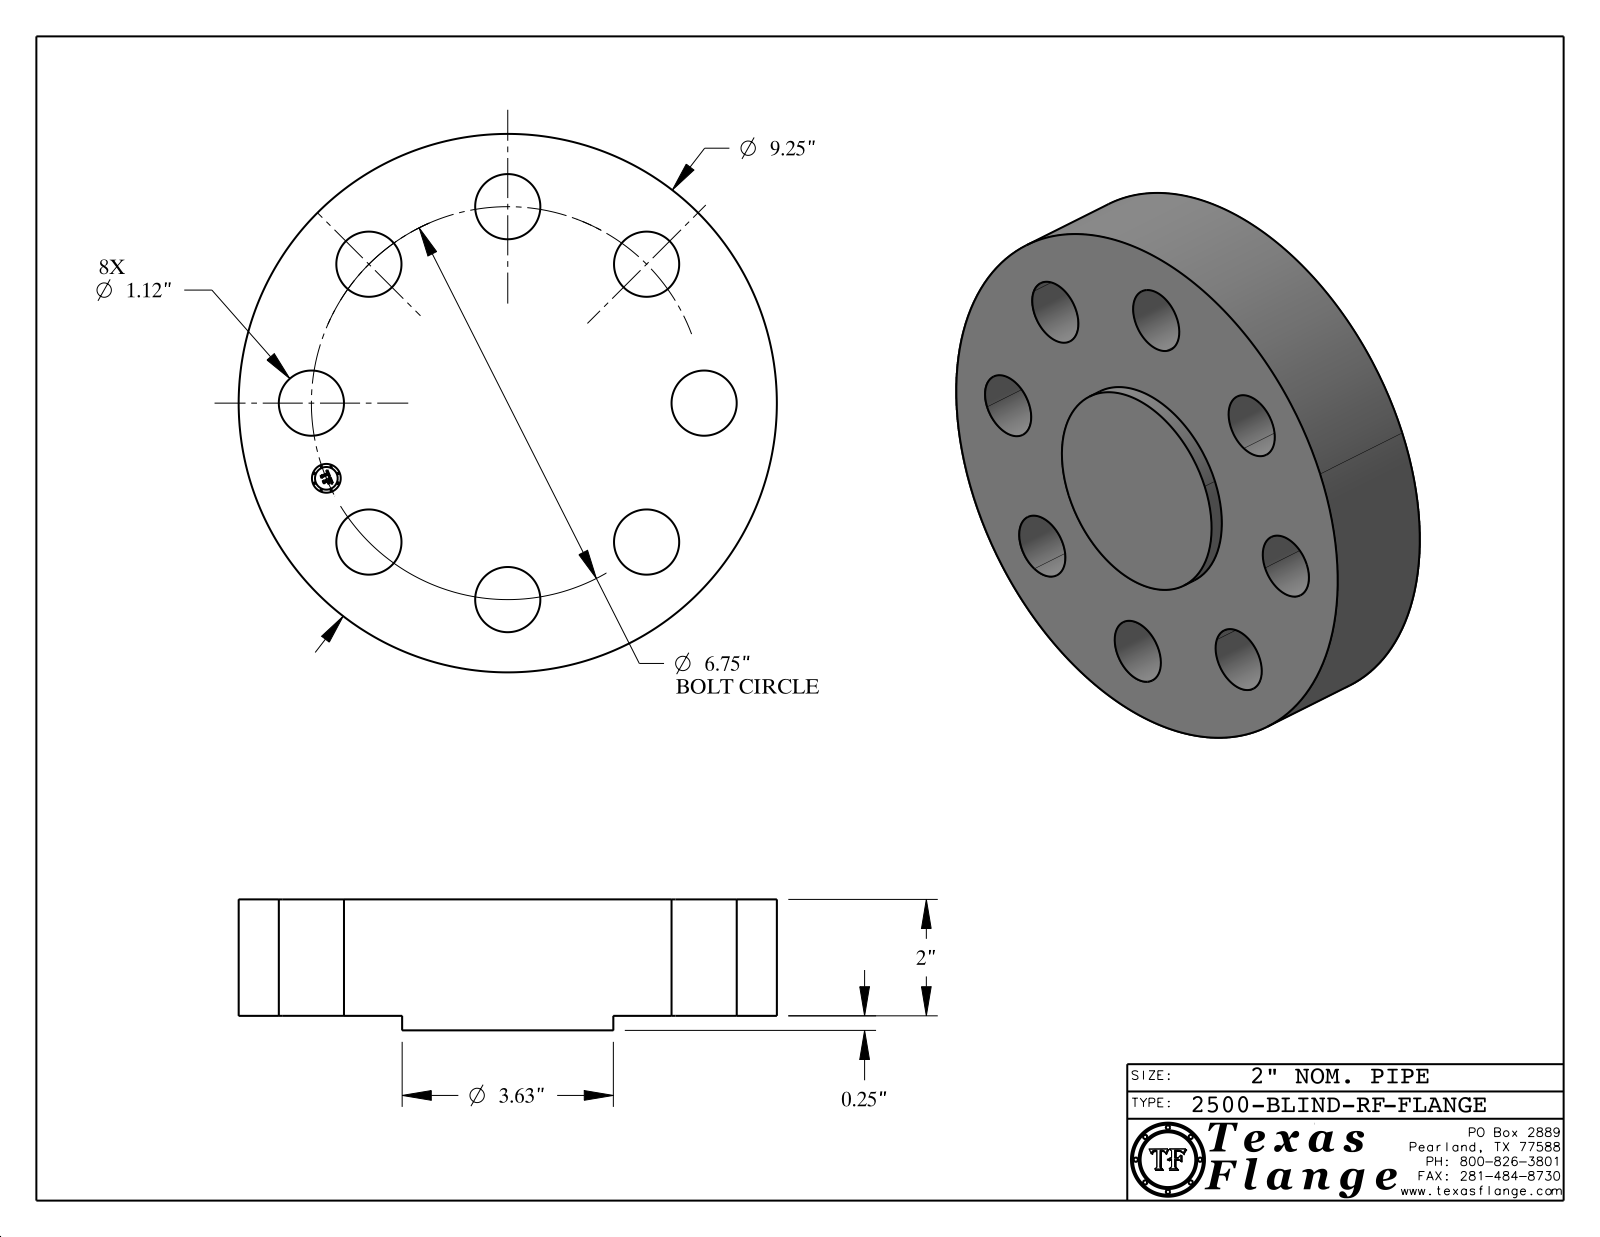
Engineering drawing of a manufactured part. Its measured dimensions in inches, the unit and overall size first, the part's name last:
Units: inches
Overall size (bounding box): 9.25 × 9.25 × 2.25
Round holes (diameter × count): ⌀1.12 ×8, ⌀0.495 ×1
Round bosses / shafts (diameter × count): ⌀0.03 ×8, ⌀9.25 ×1, ⌀3.63 ×1, ⌀0.39 ×1
Main face-to-face distances: 2, 0.25, 2.25, 2.235, 1.985, 0.015, 0.148, 0.145, 0.027, 0.096
Hole centre spacings: 2.583, 4.773, 6.237, 6.75, 1.317, 5.613, 6.62, 3.75
Volume: 121.2 in³ · Surface area: 236 in²
Bodies: 1 solid, 408 faces (368 planar, 40 cylindrical, 0 other)
Part name (STEP PRODUCT): 2500-BLIND-RF
STEP written by: CATIA V5 STEP AP214 (AUTOMOTIVE_DESIGN)
